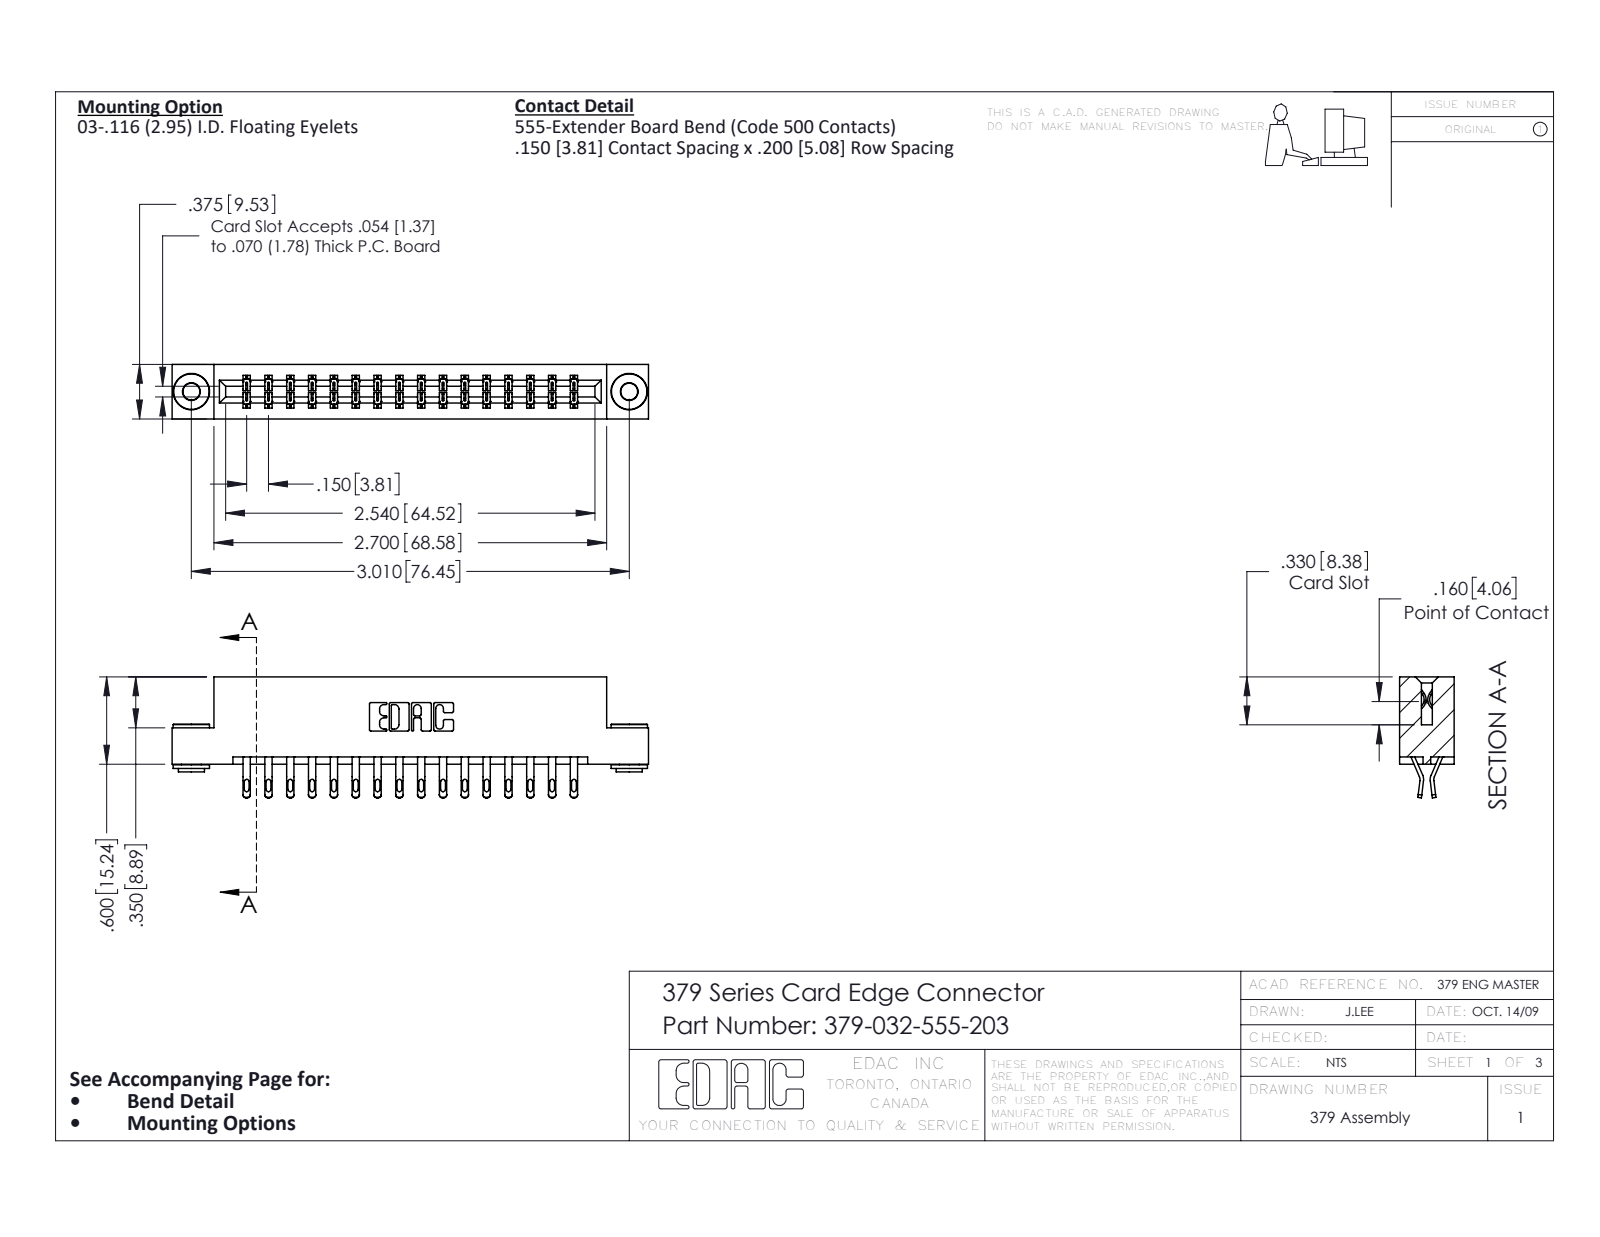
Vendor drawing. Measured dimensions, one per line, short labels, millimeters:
name: 345-250-002_345-250-002-102; 379 Part_Flush - .156 Dia - TH; 345-292-001_555 Tail; 379-032-555-203
written by: SolidWorks 2020 (CONFIG_CONTROL_DESIGN)
unit: mm
bodies: 35 solids, 2008 faces (1168 planar, 832 cylindrical, 8 other)
size: 83.2 × 21.1 × 9.5
volume: 8 650 mm³; area: 10 050 mm²
holes: 2× ⌀2.9, 2× ⌀4
bosses: 2× ⌀6.4, 2× ⌀4.6, 2× ⌀3.5
rounds: 64× R0.4, 64× R0.5, 48× R0.2, 22× R0.3, 6× R0.2, 6× R0.8, 3× R0.7, 2× R0.3
face distances: 7.6, 9.5, 5.1, 1.9, 3.8, 2.5, 1.3, 15.2, 14, 5.7
hole spacings: 76.5
